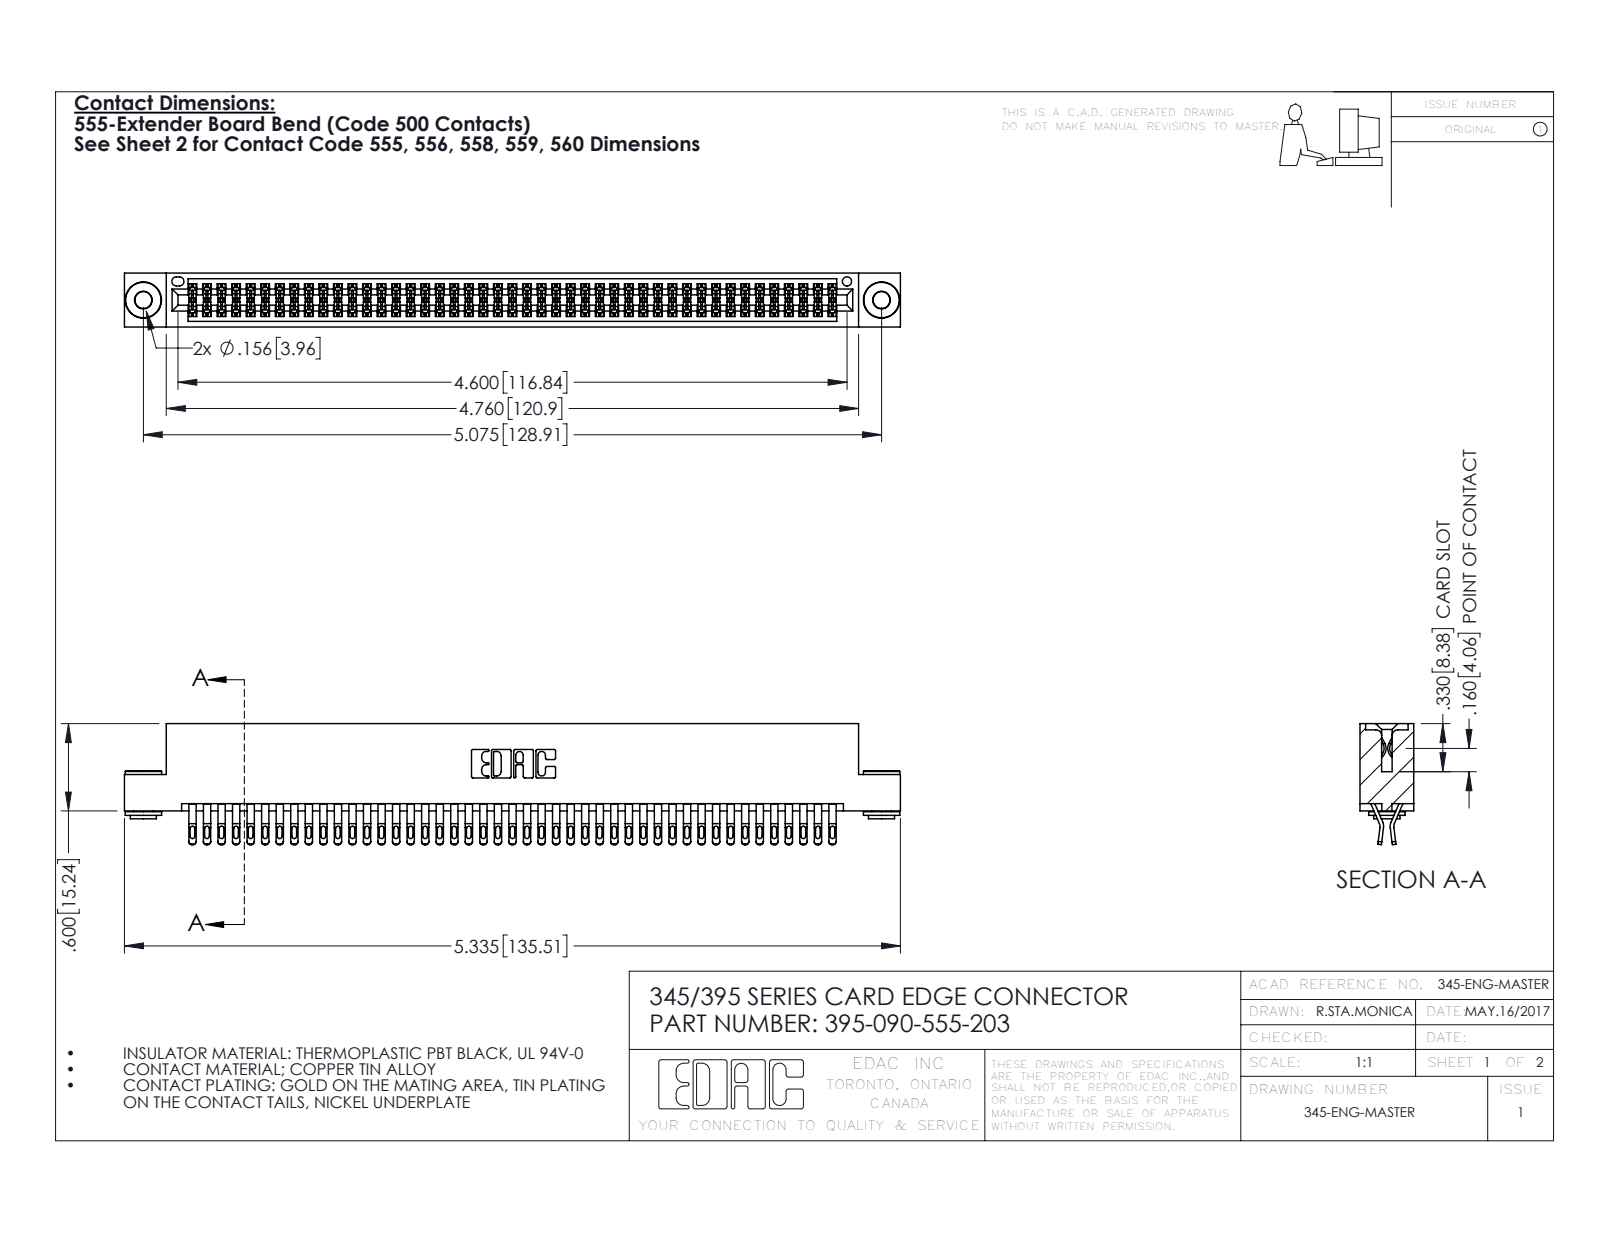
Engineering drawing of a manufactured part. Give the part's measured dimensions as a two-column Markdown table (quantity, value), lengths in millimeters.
| quantity | value |
| --- | --- |
| part name | 345 Part_Flush Mounting Lugs - 0.156 Dia-TH; 345-292-001_555 Tail; 345-250-002_345-250-002-102; 395-090-555-203 |
| STEP written by | SolidWorks 2016 (CONFIG_CONTROL_DESIGN) |
| units | millimeters |
| bodies | 93 solids, 5204 faces (2880 planar, 2316 cylindrical, 8 other) |
| overall size | 135.5 × 21.1 × 9.4 |
| volume | 13 500 mm³ |
| surface area | 21 080 mm² |
| round holes (diameter × count) | 2.9 × 2, 4 × 2, 1.6 × 1 |
| round bosses / shafts (diameter × count) | 6.4 × 2, 4.6 × 2, 3.5 × 2 |
| partial cylindrical surfaces (radius × count) | 0.4 × 225, 0.5 × 180, 0.2 × 135, 0.3 × 22, 0.2 × 6, 0.8 × 6, 0.7 × 3, 0.3 × 2 |
| main face-to-face distances | 1.8, 7.6, 0.6, 5.1, 9.4, 2.5, 6.9, 5.7, 4.4, 3.8 |
| hole center spacings | 6.9, 122.9, 128.9 |
